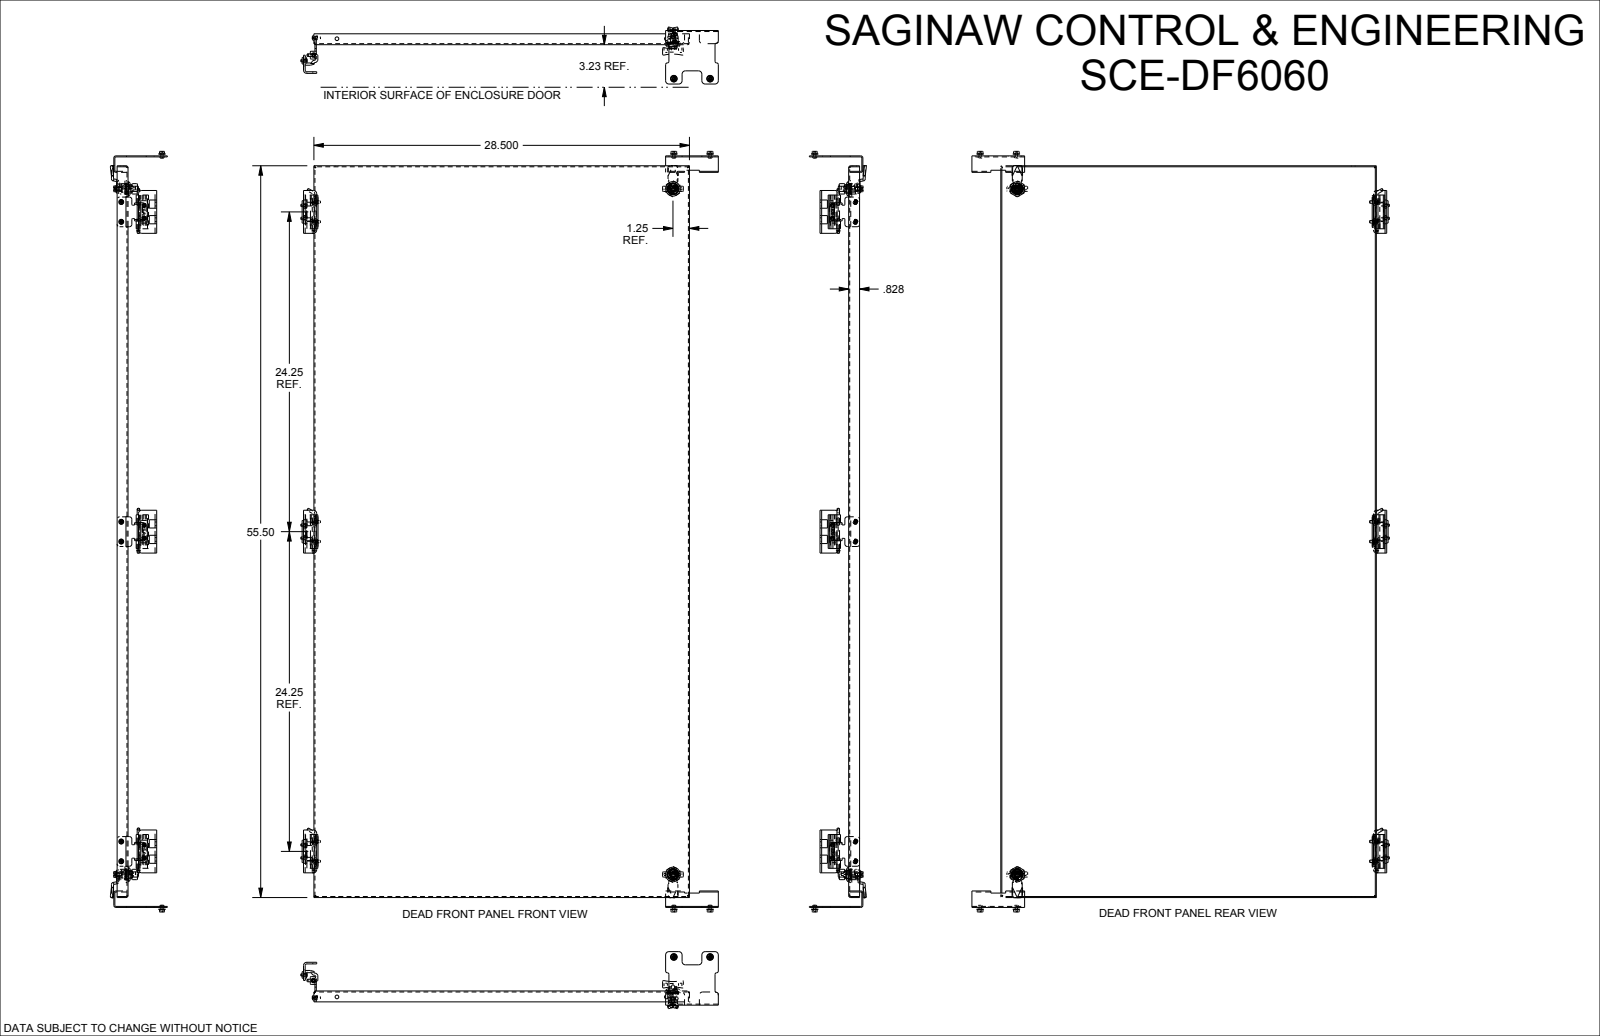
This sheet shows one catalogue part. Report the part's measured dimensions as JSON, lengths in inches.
{"part_name": "SCE-DF6060", "step_written_by": "SolidWorks 2021 (AUTOMOTIVE_DESIGN)", "units": "inches", "bodies": {"solids": 59, "faces": 2404, "planar": 1134, "cylindrical": 709, "other": 561}, "overall_size": [57.688, 31.679, 4.32], "volume_in3": 114.4, "surface_area_in2": 3682, "round_holes": [[0.19, 8], [0.172, 6], [0.21, 6], [0.244, 6], [0.25, 6], [0.266, 6], [0.197, 2], [0.315, 2], [0.394, 2], [0.433, 2], [0.634, 2], [0.222, 1]], "round_bosses_or_shafts": [[0.17, 8], [0.373, 6], [0.34, 6], [0.25, 6], [0.249, 6], [0.188, 6], [0.196, 4], [1.102, 2]], "partial_cylinders_radius": [[0.012, 56], [0.25, 23], [0.02, 22], [0.01, 20], [0.157, 16], [0.062, 14], [0.068, 9], [0.125, 9]], "face_to_face_distances": [0.06, 28.44, 0.078, 55.44, 28.5, 28.38, 0.672, 0.732, 56.112, 56.172], "hole_center_spacings": [24.25, 0.985, 1.749, 1.75, 2.13, 2.13, 48.5, 23.072]}
